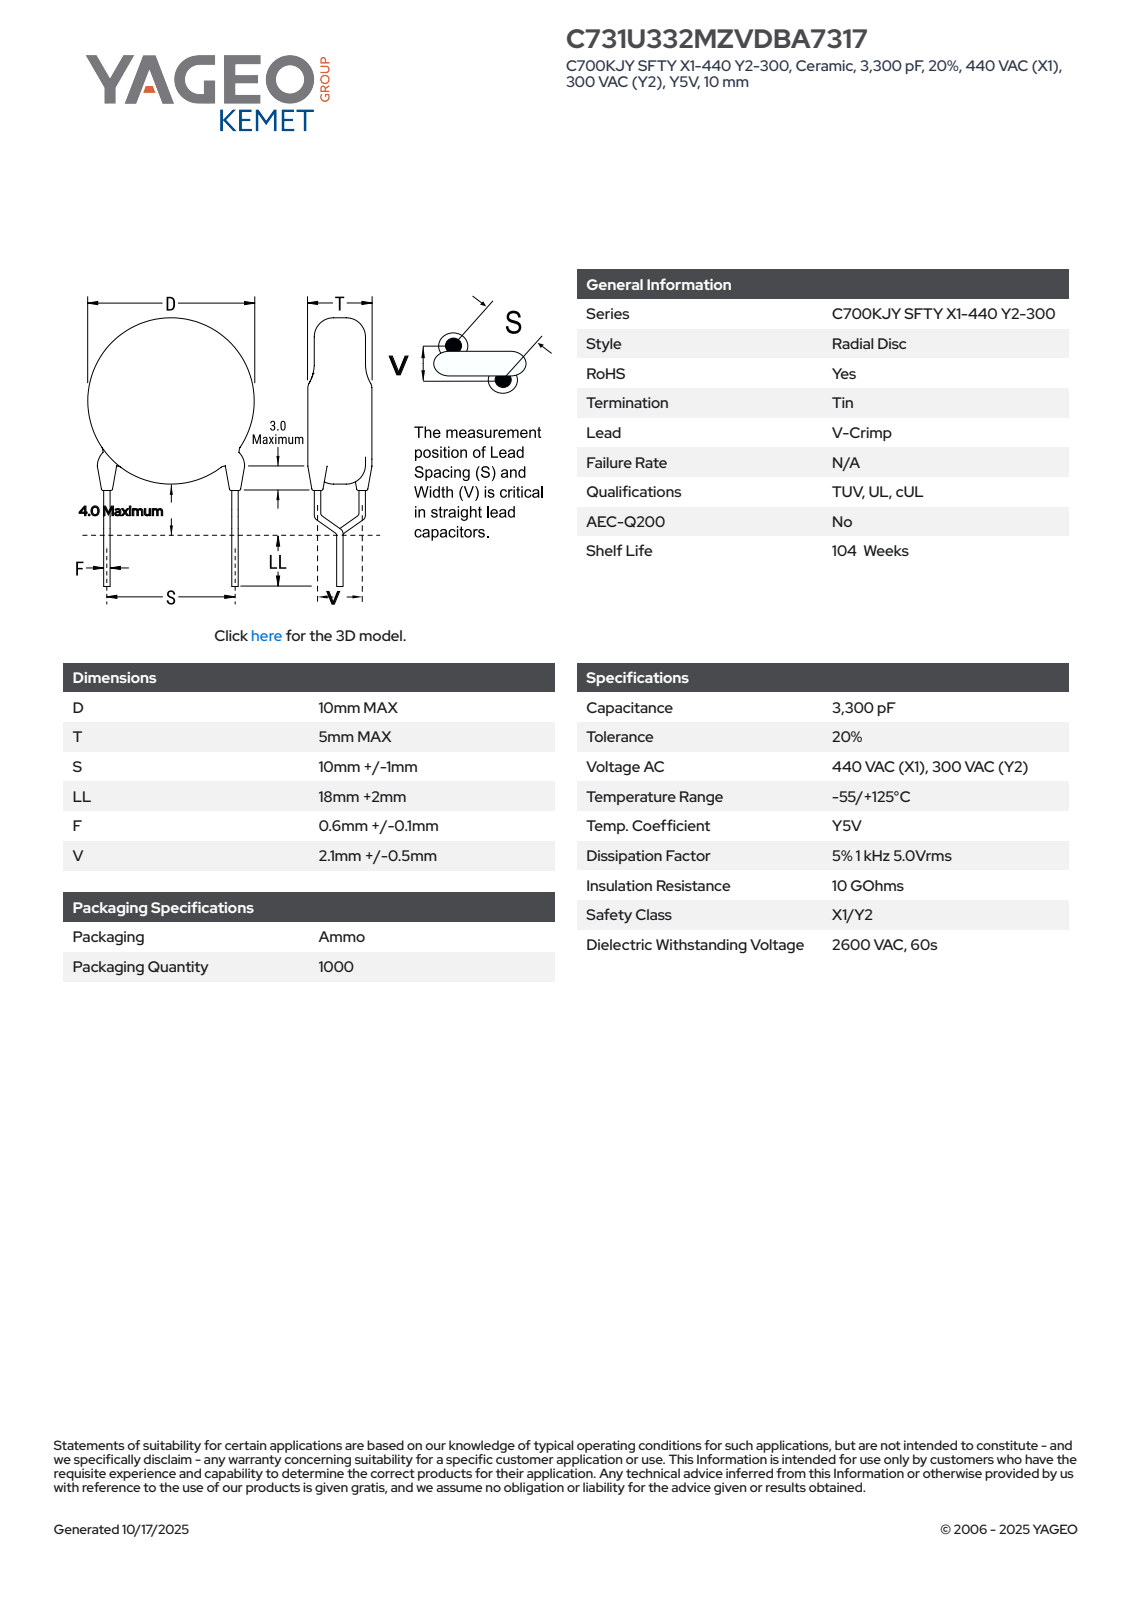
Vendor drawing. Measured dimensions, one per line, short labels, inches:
name: CCD_VC10X5_D10T5S10LL20F0.7V2.1
written by: SolidWorks 2021 (AUTOMOTIVE_DESIGN)
unit: in
bodies: 4 solids, 89 faces (63 planar, 22 cylindrical, 4 other)
size: 1.181 × 0.441 × 0.197
volume: 0.025 in³; area: 0.631 in²
bosses: 6× ⌀0.028, 4× ⌀0.047, 1× ⌀0.394
face distances: 0.197, 0.787, 1.015, 0.228, 0.968, 0.18, 0.048, 0.013, 0.039, 0.195
